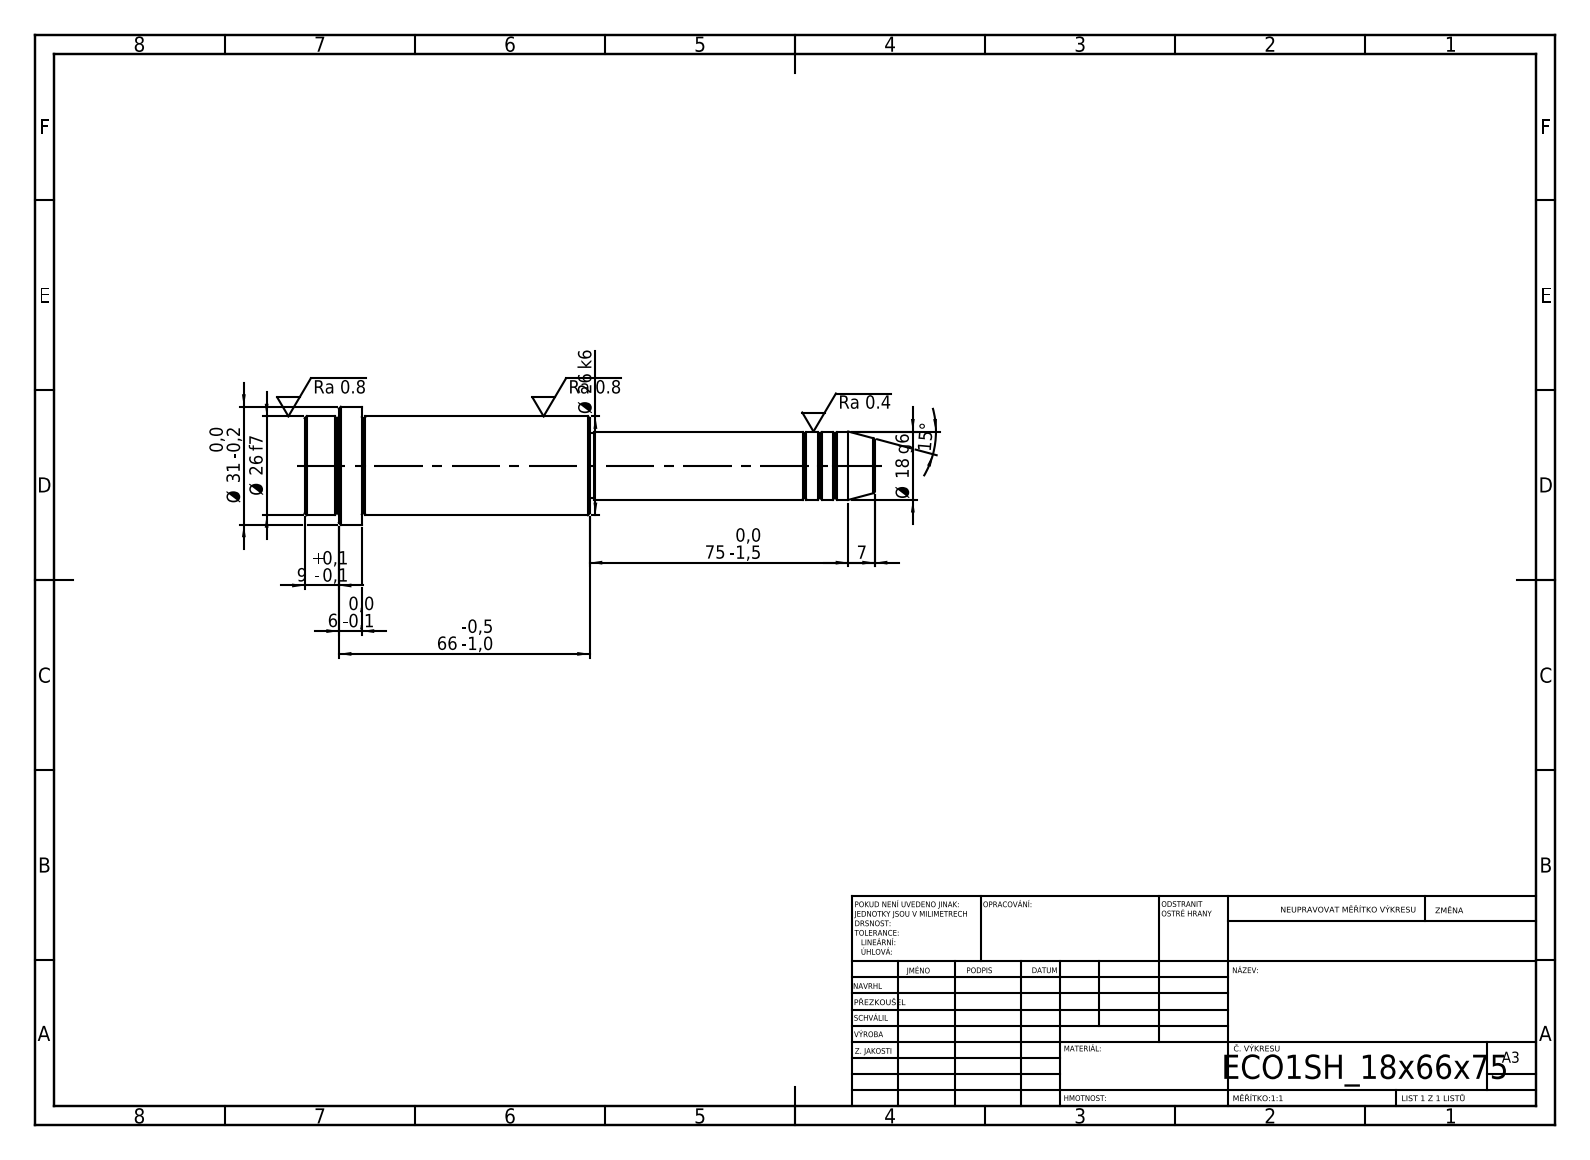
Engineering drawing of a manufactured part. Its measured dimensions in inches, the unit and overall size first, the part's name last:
Units: inches
Overall size (bounding box): 5.906 × 1.22 × 1.22
Round bosses / shafts (diameter × count): ⌀1.22 ×1, ⌀1.024 ×1, ⌀0.709 ×1, ⌀0.669 ×1
Main face-to-face distances: 2.953, 2.362, 0.591, 2.598, 0.236, 0.354, 5.315, 5.551, 5.906, 2.913
Volume: 3.644 in³ · Surface area: 18.59 in²
Bodies: 1 solid, 52 faces (6 planar, 16 cylindrical, 30 other)
STEP written by: SolidWorks 2019 (CONFIG_CONTROL_DESIGN)
